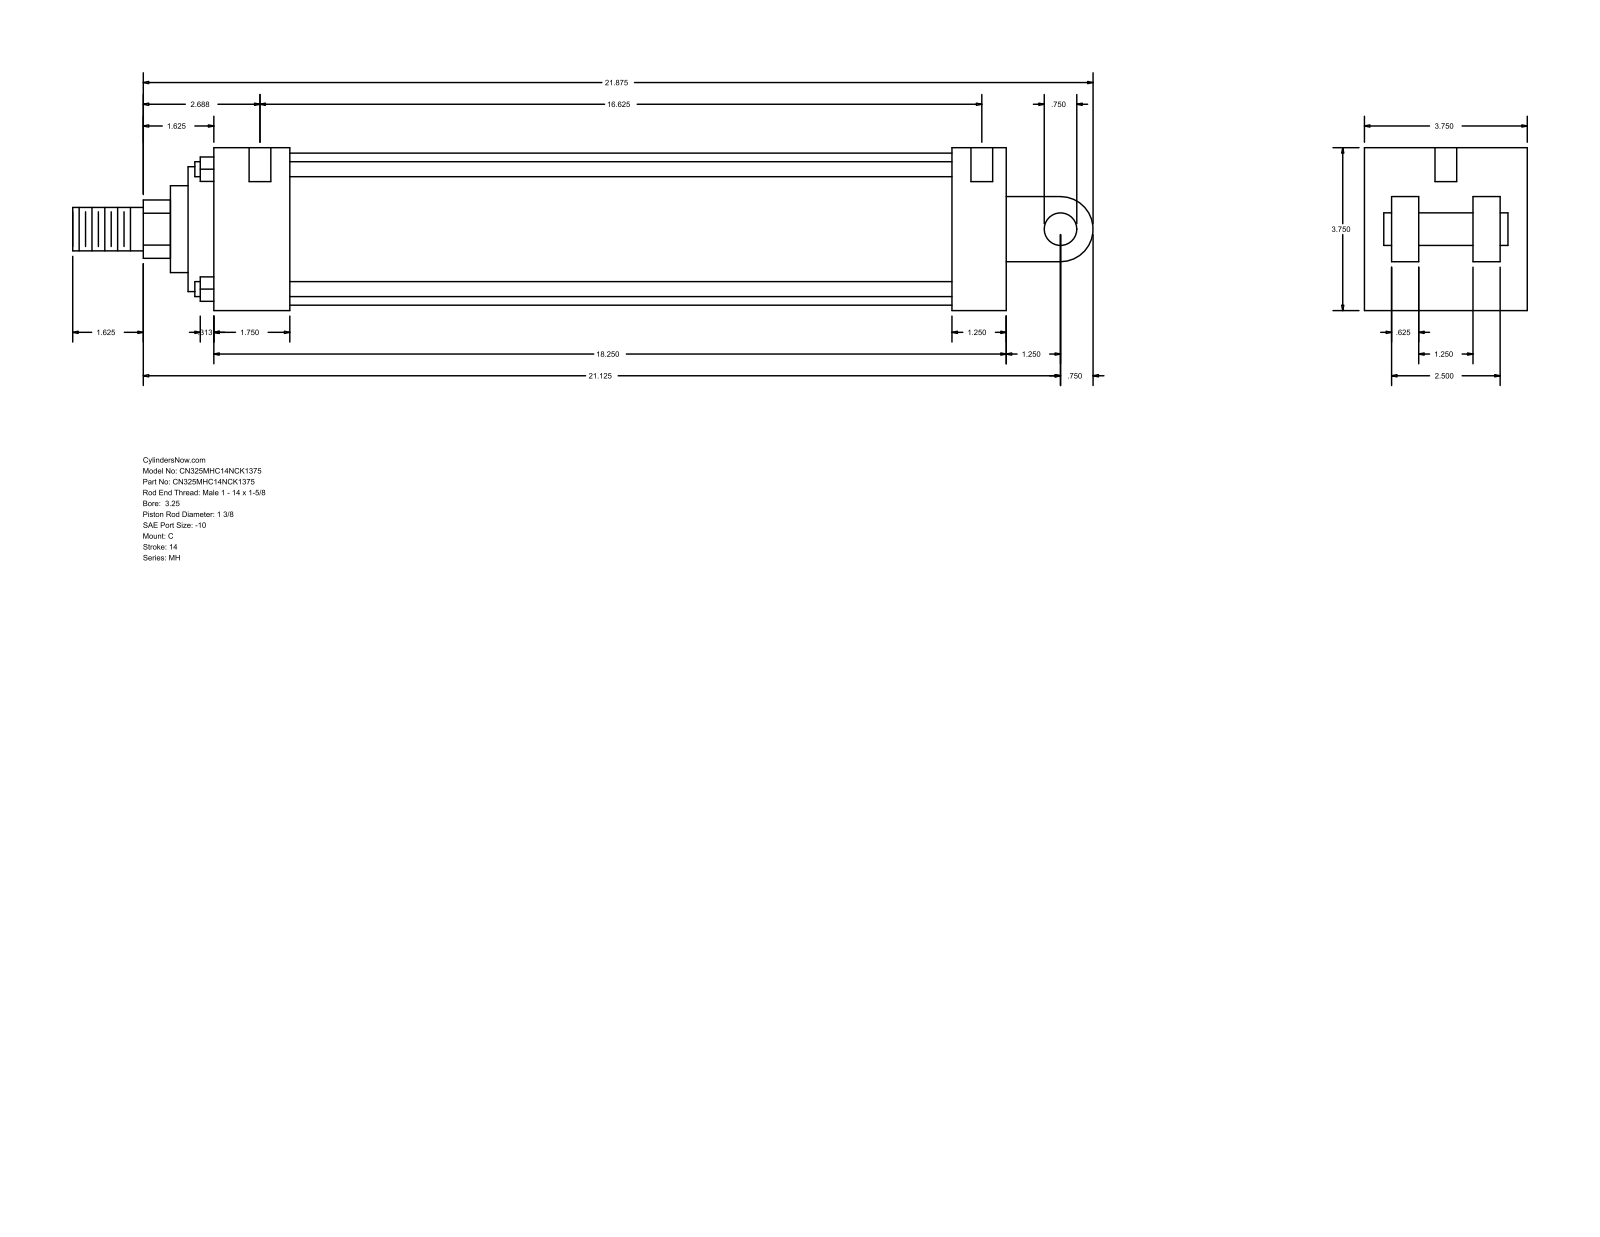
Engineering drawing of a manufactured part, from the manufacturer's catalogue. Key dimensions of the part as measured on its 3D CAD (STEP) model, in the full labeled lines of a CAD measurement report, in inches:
Part name (STEP PRODUCT): MH_C__0325_1.375
STEP written by: GSSL Pune (CONFIG_CONTROL_DESIGN)
Units: inches
Bodies: 0 solids, 101 faces (71 planar, 30 cylindrical, 0 other)
Overall size (bounding box): 23.5 × 3.75 × 3.75
Round holes (diameter × count): ⌀0.219 ×4, ⌀0.5 ×2
Round bosses / shafts (diameter × count): ⌀0.345 ×4, ⌀3.5 ×1, ⌀2.875 ×1, ⌀2 ×1, ⌀1.375 ×1, ⌀1 ×1, ⌀0.75 ×1
Partial cylindrical surfaces — rounded edges, fillets, slot ends (radius × count): R0.672 ×1, R0.75 ×1
Main face-to-face distances: 3.75, 0.625, 2.5, 18.25, 1.25, 3.125, 1.875, 1.75, 17, 15.25
Hole centre spacings: 16.875, 0.063, 0.187, 16.625, 16.688, 16.813
